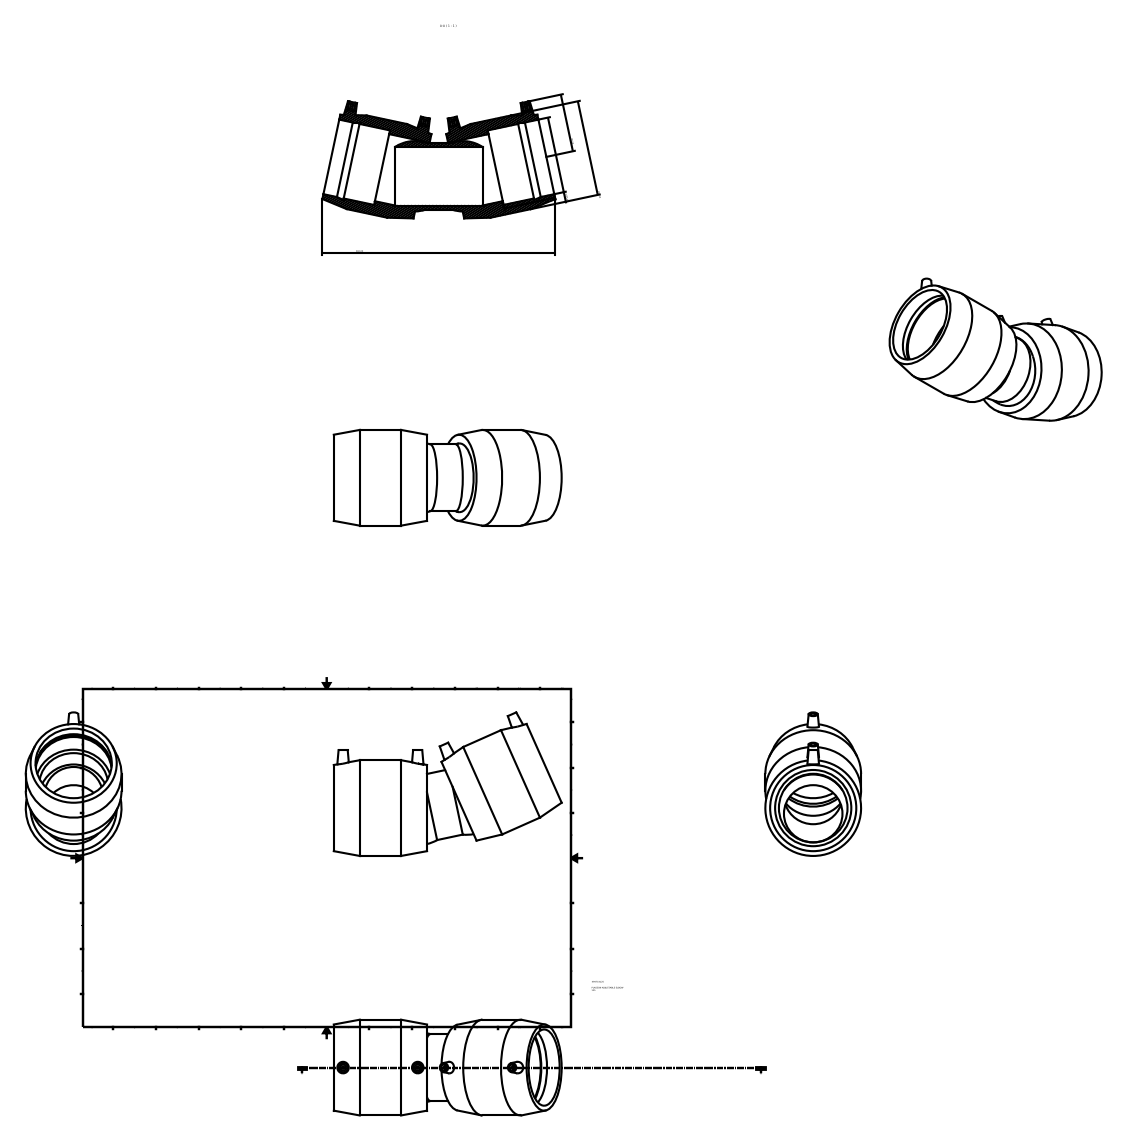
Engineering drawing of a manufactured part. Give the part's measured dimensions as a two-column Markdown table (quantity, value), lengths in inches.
| quantity | value |
| --- | --- |
| part name | 4947C4125 |
| STEP written by | Autodesk Inventor 2015 (AUTOMOTIVE_DESIGN) |
| units | inches |
| bodies | 1 solid, 50 faces (20 planar, 18 cylindrical, 12 other) |
| overall size | 14.711 × 9.269 × 6.181 |
| volume | 151.2 in³ |
| surface area | 560.5 in² |
| round holes (diameter × count) | 0.394 × 4, 4.921 × 3, 4.429 × 2, 3.778 × 1 |
| round bosses / shafts (diameter × count) | 0.157 × 4, 6.181 × 2, 4.311 × 1 |
| main face-to-face distances | 6.016, 6.019, 3.346, 2.669, 2.67, 3.348, 1.339, 2.008, 4.677, 4.68 |
| hole center spacings | 4.813 |
